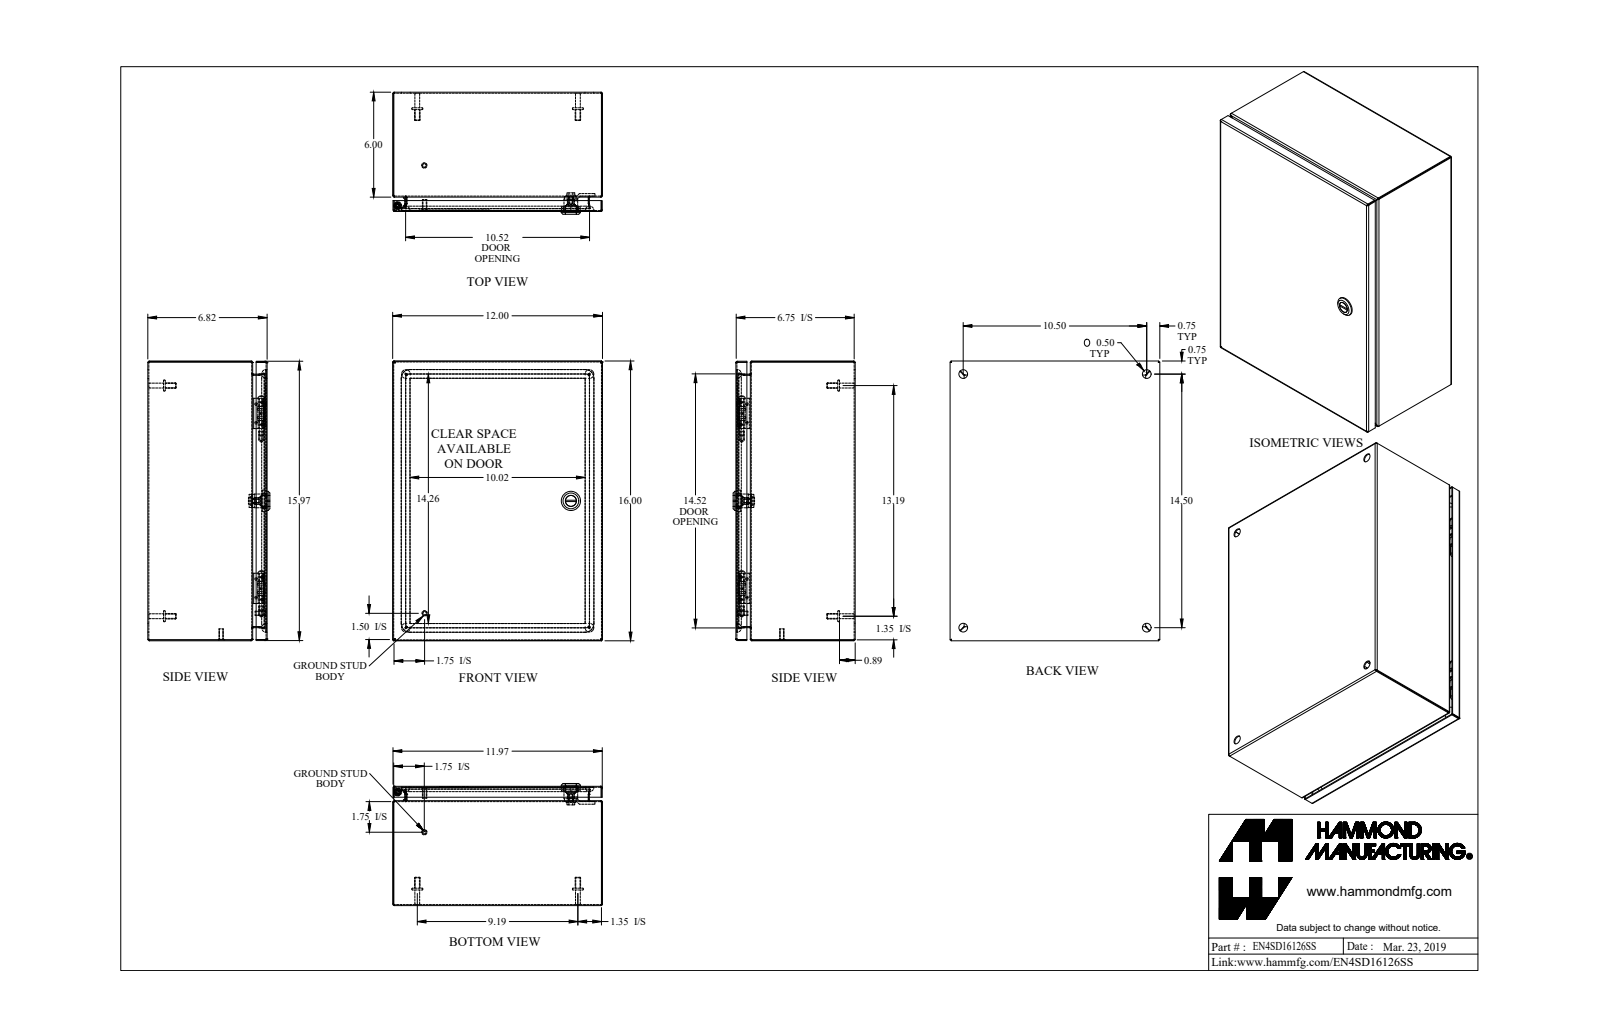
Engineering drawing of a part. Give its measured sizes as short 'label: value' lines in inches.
name: EN4SD16126SS_Default
written by: SolidWorks 2019 (CONFIG_CONTROL_DESIGN)
unit: in
bodies: 22 solids, 657 faces (303 planar, 212 cylindrical, 142 other)
size: 16 × 12 × 6.982
volume: 53.03 in³; area: 1 788 in²
holes: 5× ⌀0.5, 1× ⌀0.172, 1× ⌀0.197, 1× ⌀0.24, 1× ⌀0.242, 1× ⌀0.387, 1× ⌀0.63, 1× ⌀0.768
bosses: 6× ⌀0.313, 5× ⌀0.625, 4× ⌀0.275, 2× ⌀0.25, 1× ⌀1.1, 1× ⌀0.785, 1× ⌀0.525, 1× ⌀0.455
rounds: 21× R0.029, 21× R0.086, 12× R0.188, 4× R0.006, 4× R0.062, 4× R0.25, 4× R0.499, 2× R0.125
face distances: 0.057, 6.765, 6.708, 6.822, 11.943, 15.943, 11.886, 12, 15.886, 16
hole spacings: 7.327, 10.5, 11.904, 14.5, 17.902
